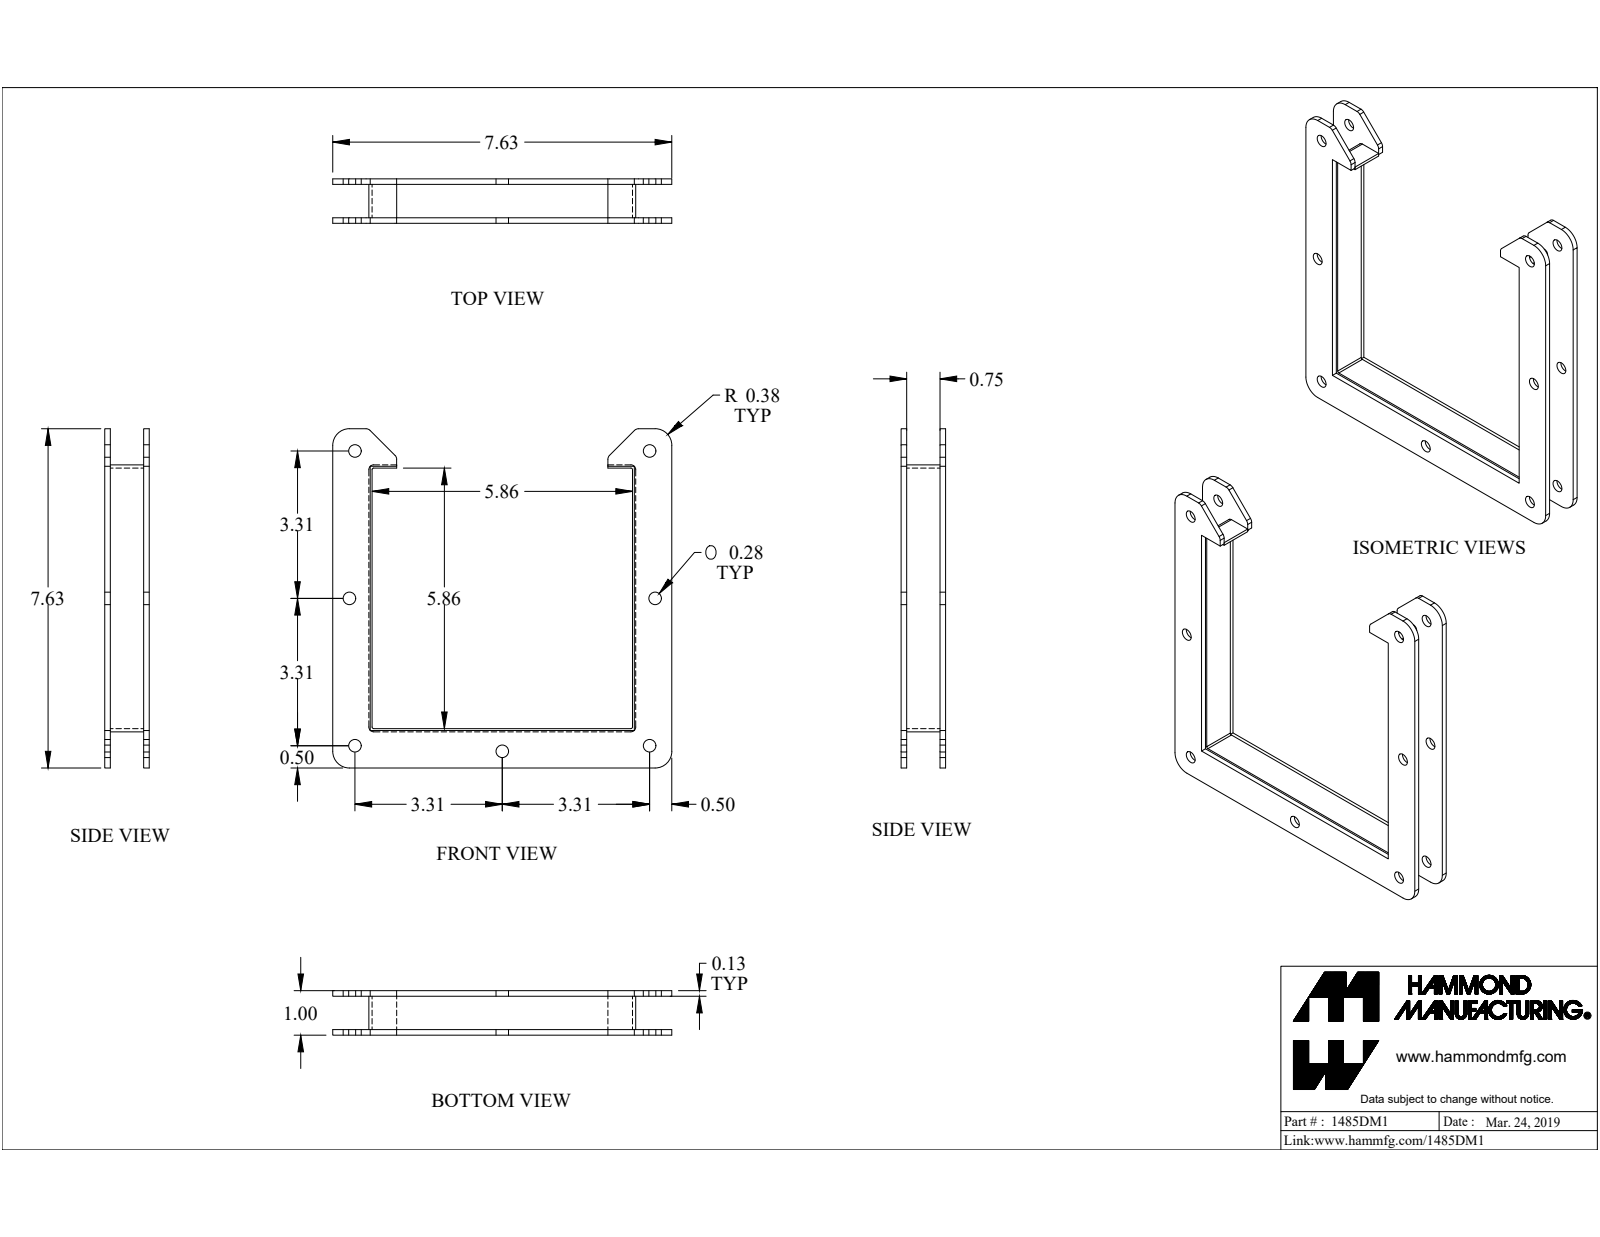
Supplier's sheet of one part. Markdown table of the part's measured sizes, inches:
| quantity | value |
| --- | --- |
| part name | 1485DM1 |
| STEP written by | SolidWorks 2019 (CONFIG_CONTROL_DESIGN) |
| units | inches |
| bodies | 3 solids, 84 faces (46 planar, 38 cylindrical, 0 other) |
| overall size | 7.625 × 7.625 × 1 |
| volume | 5.494 in³ |
| surface area | 115.5 in² |
| round holes (diameter × count) | 0.281 × 7 |
| partial cylindrical surfaces (radius × count) | 0.036 × 4, 0.108 × 4, 0.125 × 4, 0.375 × 4 |
| main face-to-face distances | 0.875, 0.125, 0.875, 1, 0.75, 0.125, 0.072, 5.928, 6, 5.856 |
| hole center spacings | 7.519, 6.625, 3.315, 3.315, 9.369, 4.861, 4.862, 6.875 |
